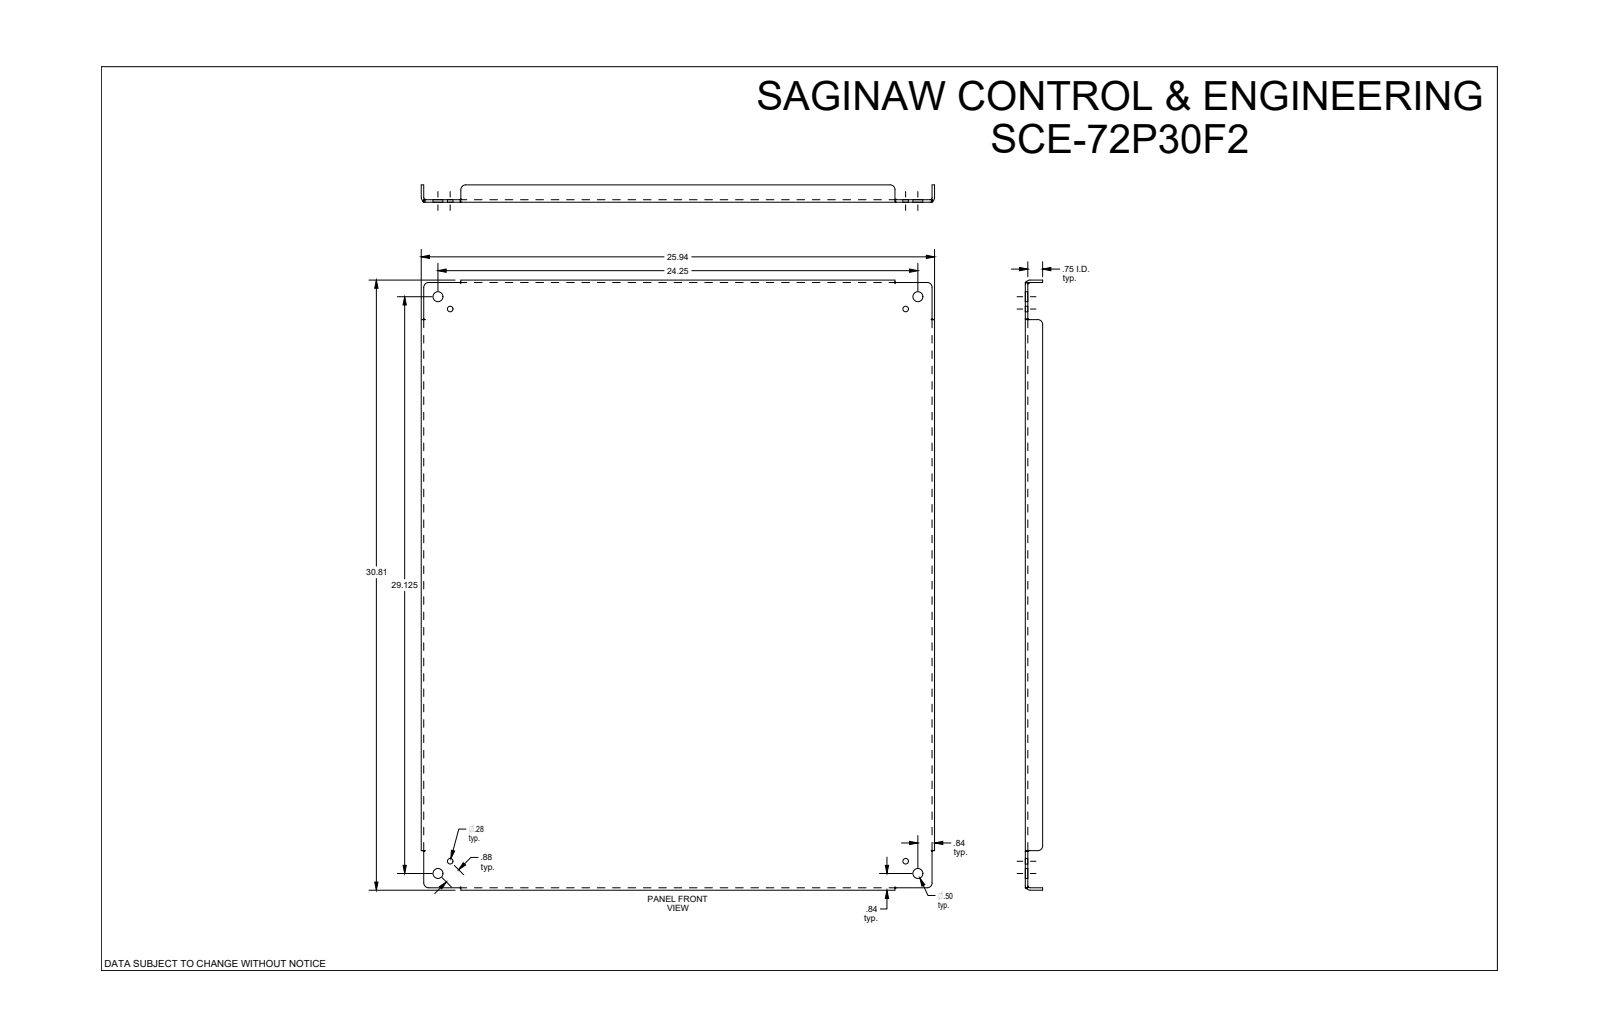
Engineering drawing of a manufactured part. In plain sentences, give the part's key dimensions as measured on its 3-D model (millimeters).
The part is named "SCE-72P30F2". Its 3-D file was written by "SolidWorks 2019 (CONFIG_CONTROL_DESIGN)". It is 1 solid with 82 faces: 30 planar, 28 cylindrical and 24 other. Overall it measures 782.7 by 658.8 by 22.2 millimeters. Its volume is 1 765 000 cubic millimeters and its surface area 1 123 000 square millimeters. Round holes: 4 of diameter 7.1, 4 of diameter 12.7. Partial cylindrical surfaces (rounded edges, fillets, slot ends): 8 of radius 6.4, 4 of radius 2.8, 4 of radius 6. The main face-to-face distances are 3.2, 3.2, 655.7, 779.4, 652.4, 658.8, 776.3, 782.7, 19.1, 22.2. The hole center spacings are 22.2, 600.4, 724.2, 940.5, 584.5, 616, 708.3, 739.8.
